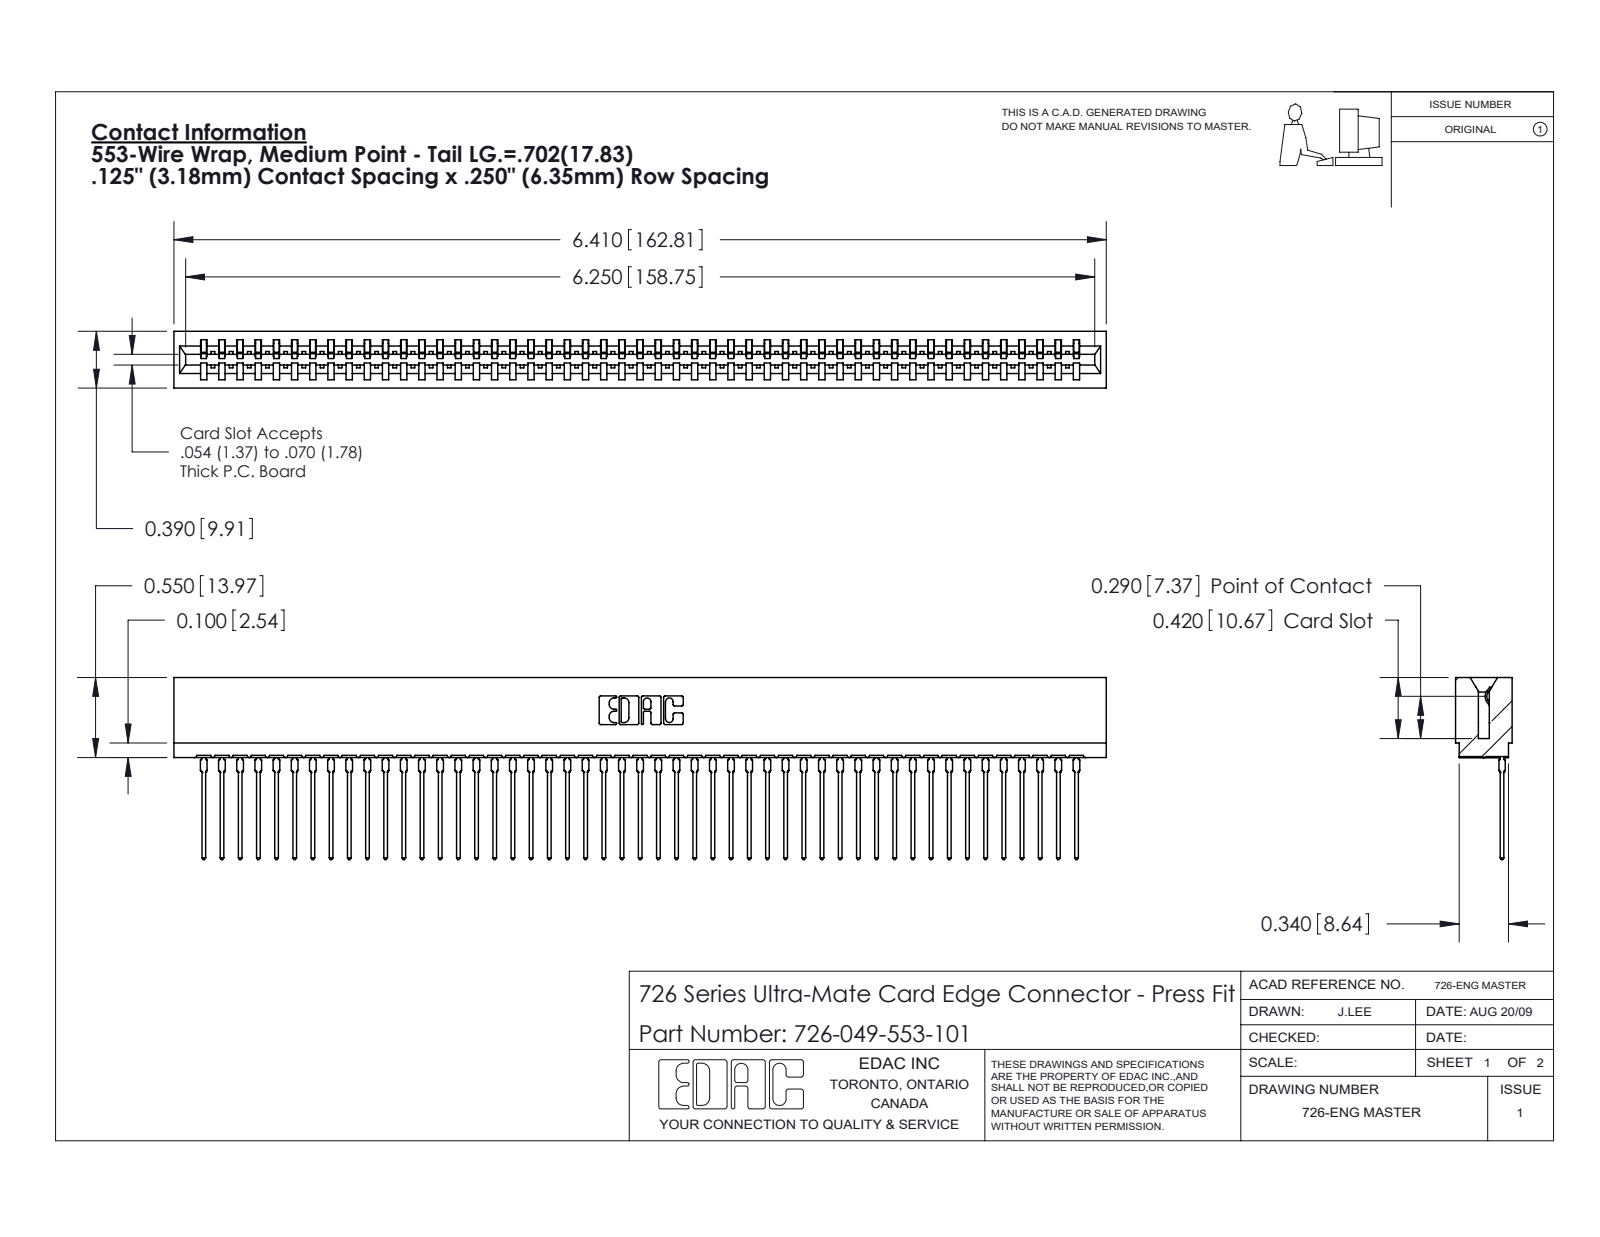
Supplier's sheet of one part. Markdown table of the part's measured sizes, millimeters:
| quantity | value |
| --- | --- |
| part name | 726 Part_.515 Slot Depth - 01; 746-292-001_553; 726-049-553-101 |
| STEP written by | SolidWorks 2020 (CONFIG_CONTROL_DESIGN) |
| units | millimeters |
| bodies | 50 solids, 5389 faces (3142 planar, 973 cylindrical, 1274 other) |
| overall size | 162.8 × 31.8 × 9.9 |
| volume | 14 700 mm³ |
| surface area | 23 410 mm² |
| partial cylindrical surfaces (radius × count) | 0.5 × 98, 0.4 × 50, 0.3 × 22, 0.2 × 6, 0.8 × 6, 0.1 × 4, 0.3 × 4, 0.7 × 3 |
| main face-to-face distances | 1.4, 8.5, 9.9, 0.6, 7.8, 6.4, 2.1, 7, 9.3, 0.8 |
